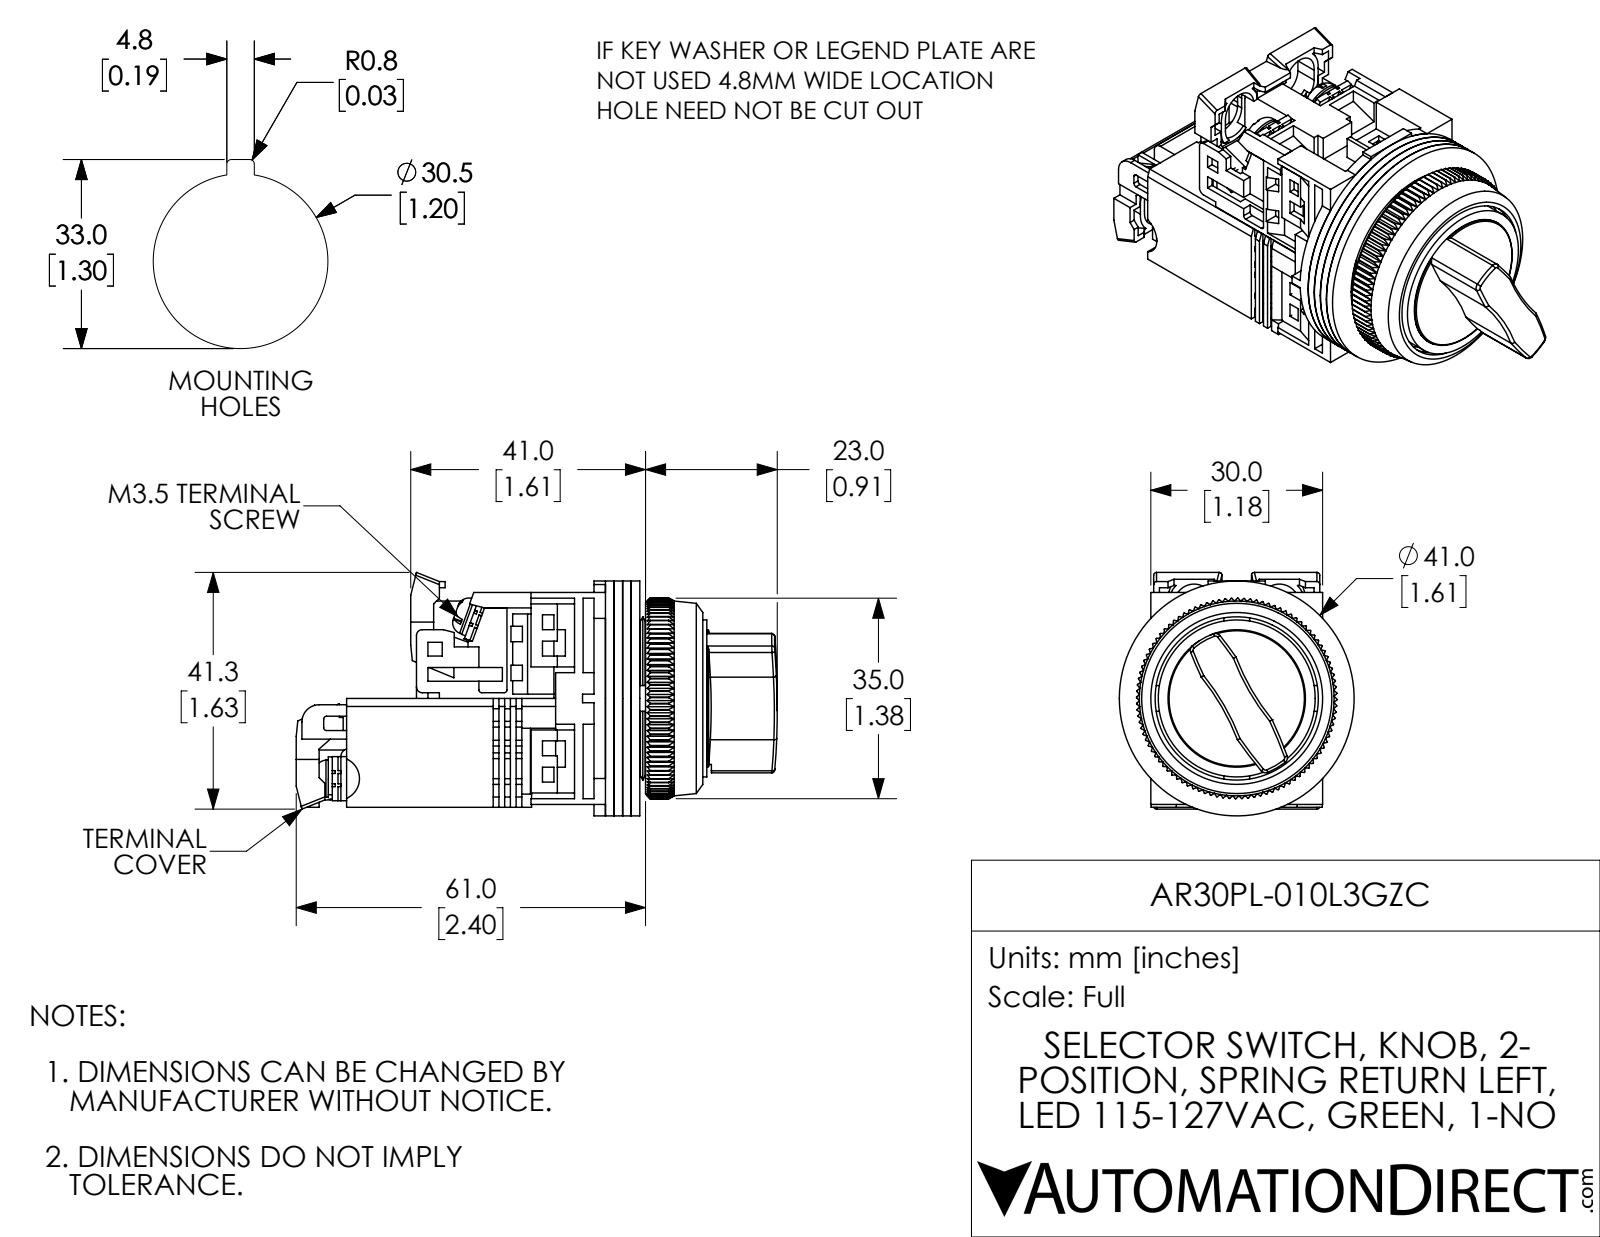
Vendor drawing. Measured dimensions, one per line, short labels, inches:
name: AR30PL-010L3GZC
written by: SolidWorks 2017 (AUTOMOTIVE_DESIGN)
unit: in
bodies: 27 solids, 2357 faces (1706 planar, 321 cylindrical, 330 other)
size: 3.307 × 1.673 × 1.614
volume: 3.001 in³; area: 63.38 in²
holes: 6× ⌀0.138, 4× ⌀0.142, 3× ⌀0.118, 1× ⌀0.472, 1× ⌀0.709, 1× ⌀0.768, 1× ⌀0.827, 1× ⌀1.122, 1× ⌀1.181, 1× ⌀1.252
bosses: 4× ⌀0.26, 2× ⌀0.138, 2× ⌀0.063, 1× ⌀1.614, 1× ⌀1.15, 1× ⌀1.079, 1× ⌀0.945, 1× ⌀0.886
rounds: 17× R0.059, 13× R0.02, 6× R0.039, 4× R0.138, 4× R0.177, 2× R0.118, 2× R1.575, 2× R2.953
face distances: 0.059, 0.118, 0.177, 0.079, 0.039, 0.748, 0.787, 0.197, 0.256, 1.417
hole spacings: 0.579, 0.297, 0.624, 0.02, 0.302, 0.583, 0.583, 0.606
